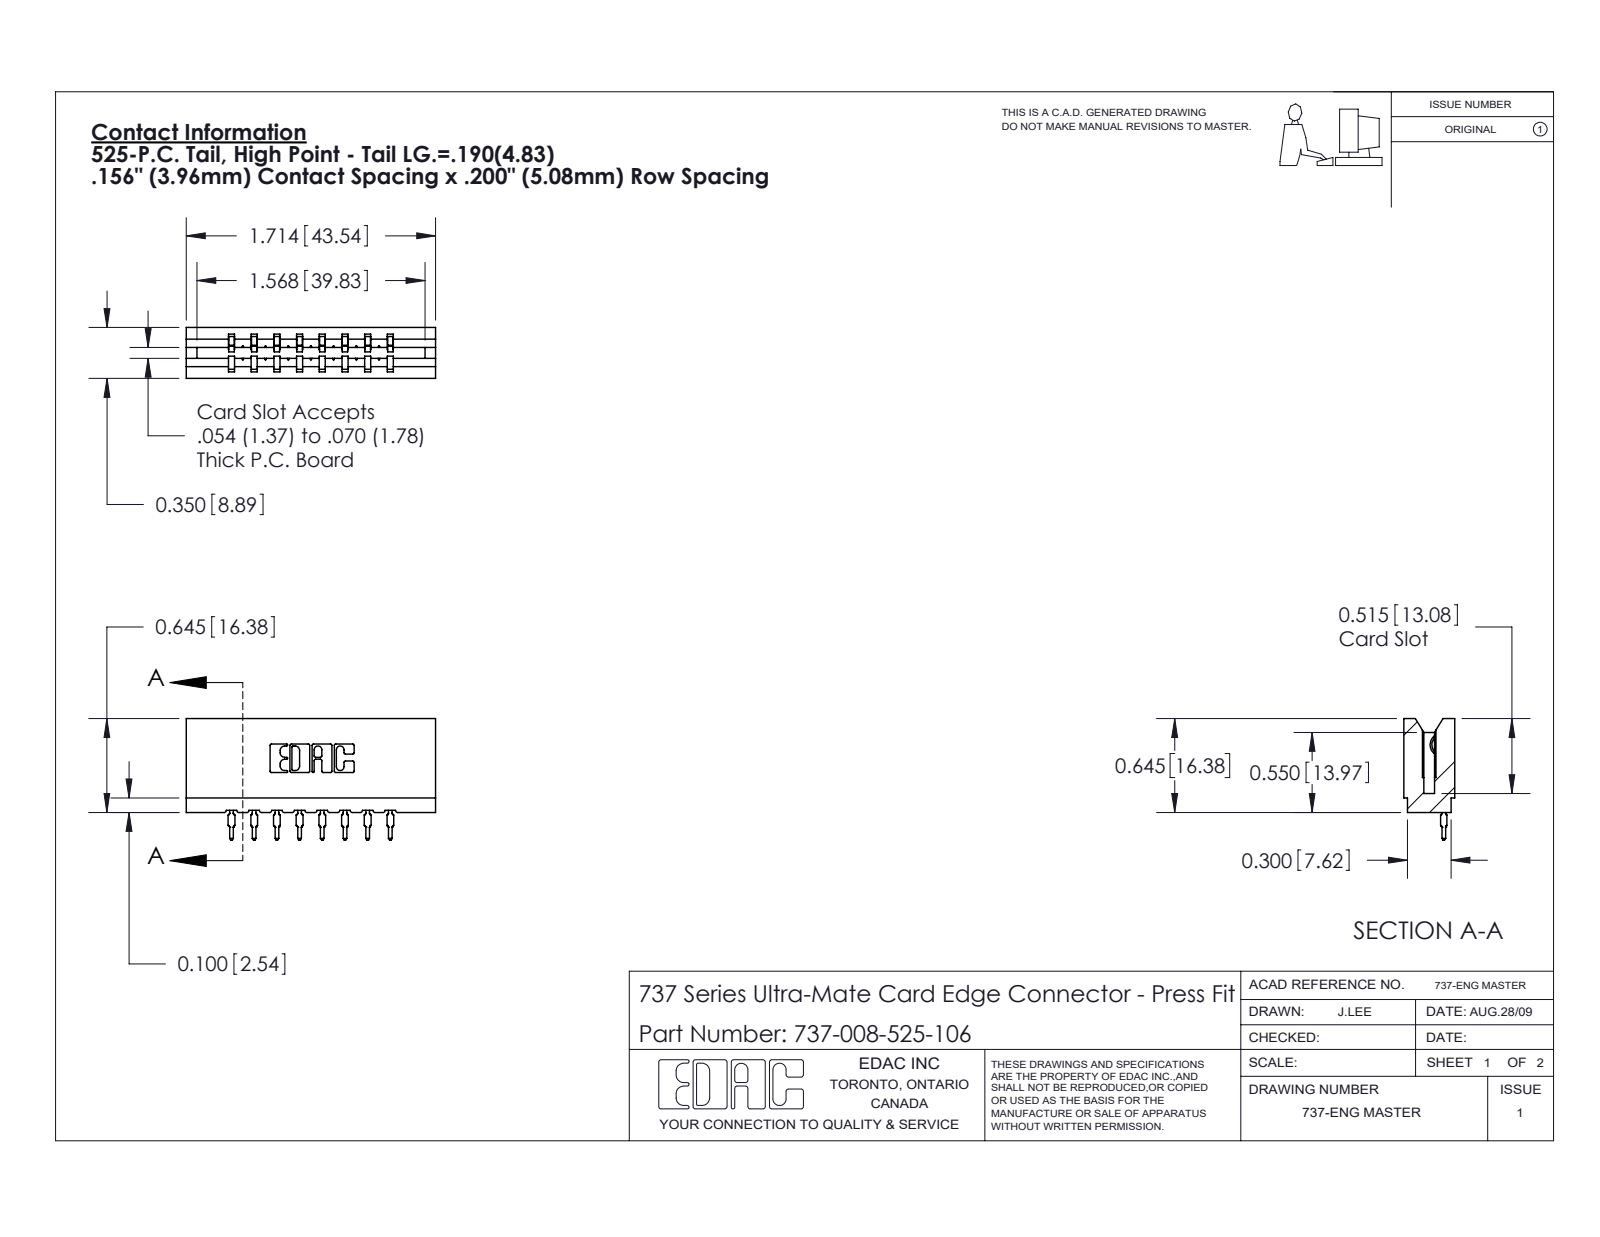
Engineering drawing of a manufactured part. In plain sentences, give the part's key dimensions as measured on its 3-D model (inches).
The part is named "737 Part_Insulator Option - 06; 745-292-001_525; 737-008-525-106". Its 3-D file was written by "SolidWorks 2020 (CONFIG_CONTROL_DESIGN)". It is 9 solids with 999 faces: 599 planar, 192 cylindrical and 208 other. Overall it measures 1.714 by 0.836 by 0.35 inches. Its volume is 0.27 cubic inches and its surface area 8.203 square inches. Partial cylindrical surfaces (rounded edges, fillets, slot ends): 22 of radius 0.01, 16 of radius 0.015, 16 of radius 0.021, 6 of radius 0.007, 6 of radius 0.031, 4 of radius 0.005, 4 of radius 0.011, 3 of radius 0.026. The main face-to-face distances are 0.156, 0.138, 0.212, 0.35, 0.312, 0.624, 0.354, 0.468, 0.78, 0.198.
